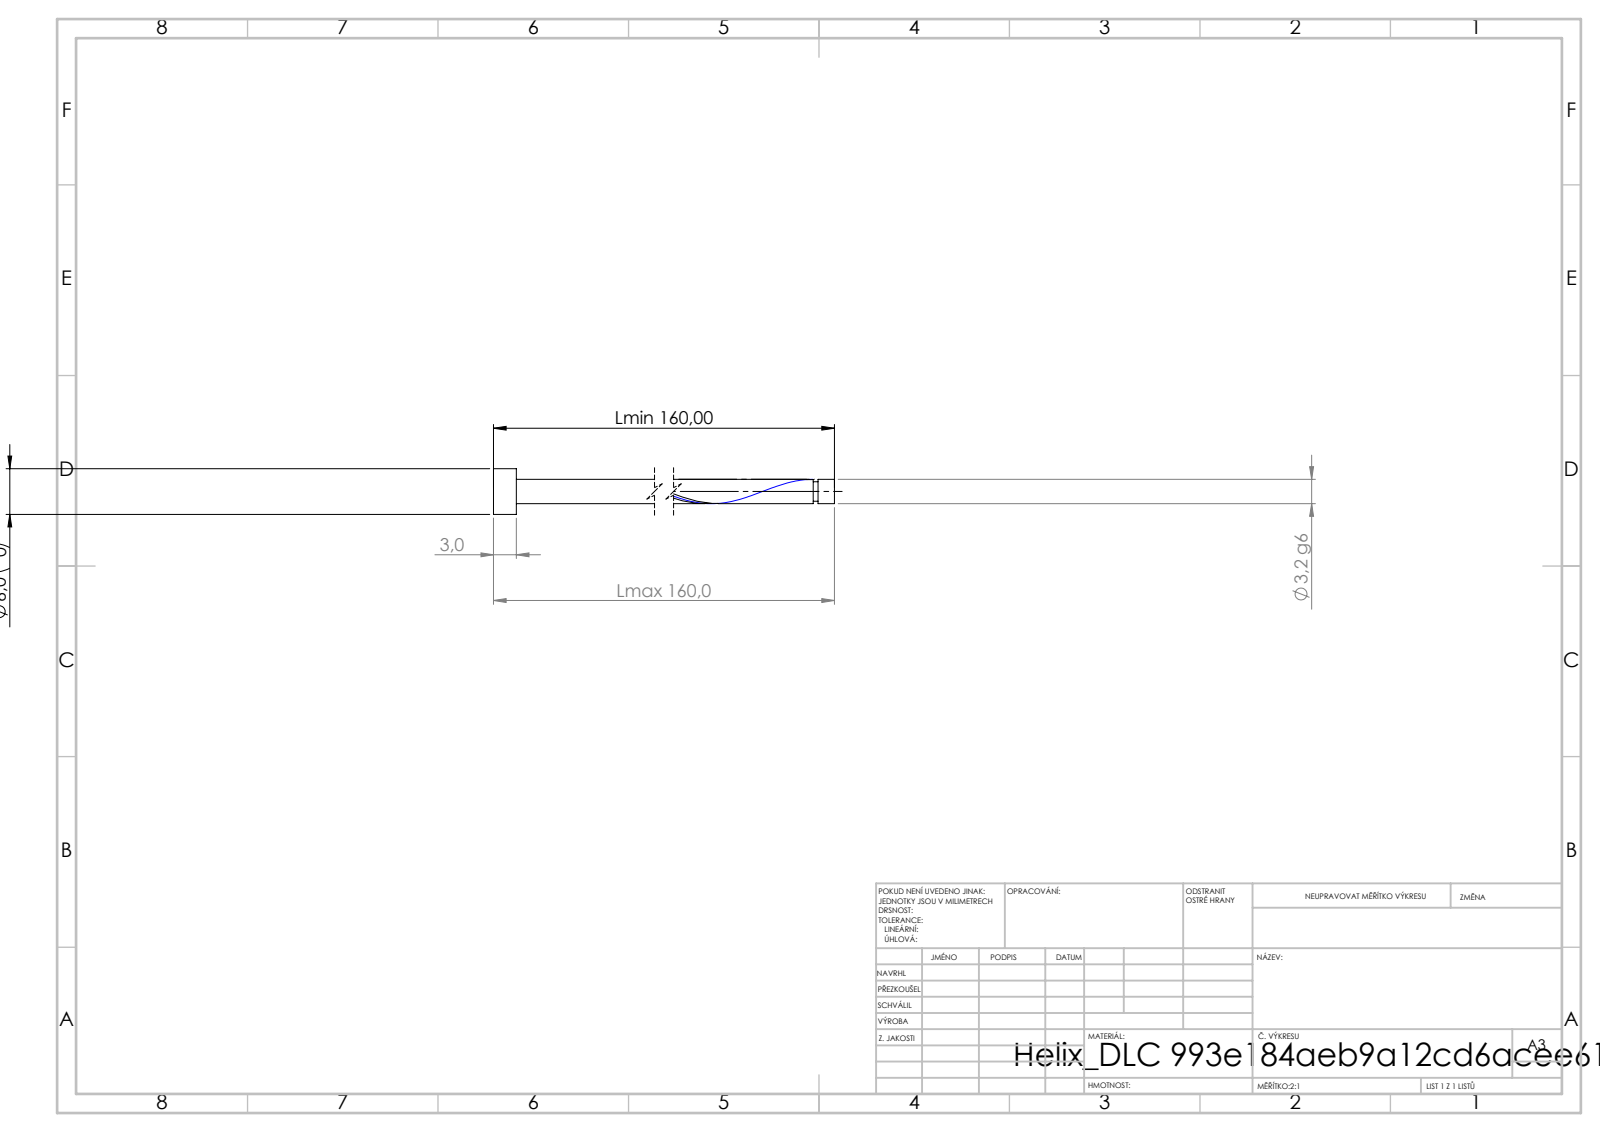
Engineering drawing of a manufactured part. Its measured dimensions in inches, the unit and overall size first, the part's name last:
Units: inches
Overall size (bounding box): 6.299 × 0.236 × 0.236
Round bosses / shafts (diameter × count): ⌀0.236 ×1, ⌀0.126 ×1, ⌀0.101 ×1
Main face-to-face distances: 0.118, 6.299, 6.181, 6.214, 6.096, 0.085, 6.189, 6.071, 0.025, 0.11
Volume: 0.081 in³ · Surface area: 2.669 in²
Bodies: 1 solid, 21 faces (6 planar, 14 cylindrical, 1 other)
STEP written by: SolidWorks 2019 (CONFIG_CONTROL_DESIGN)
